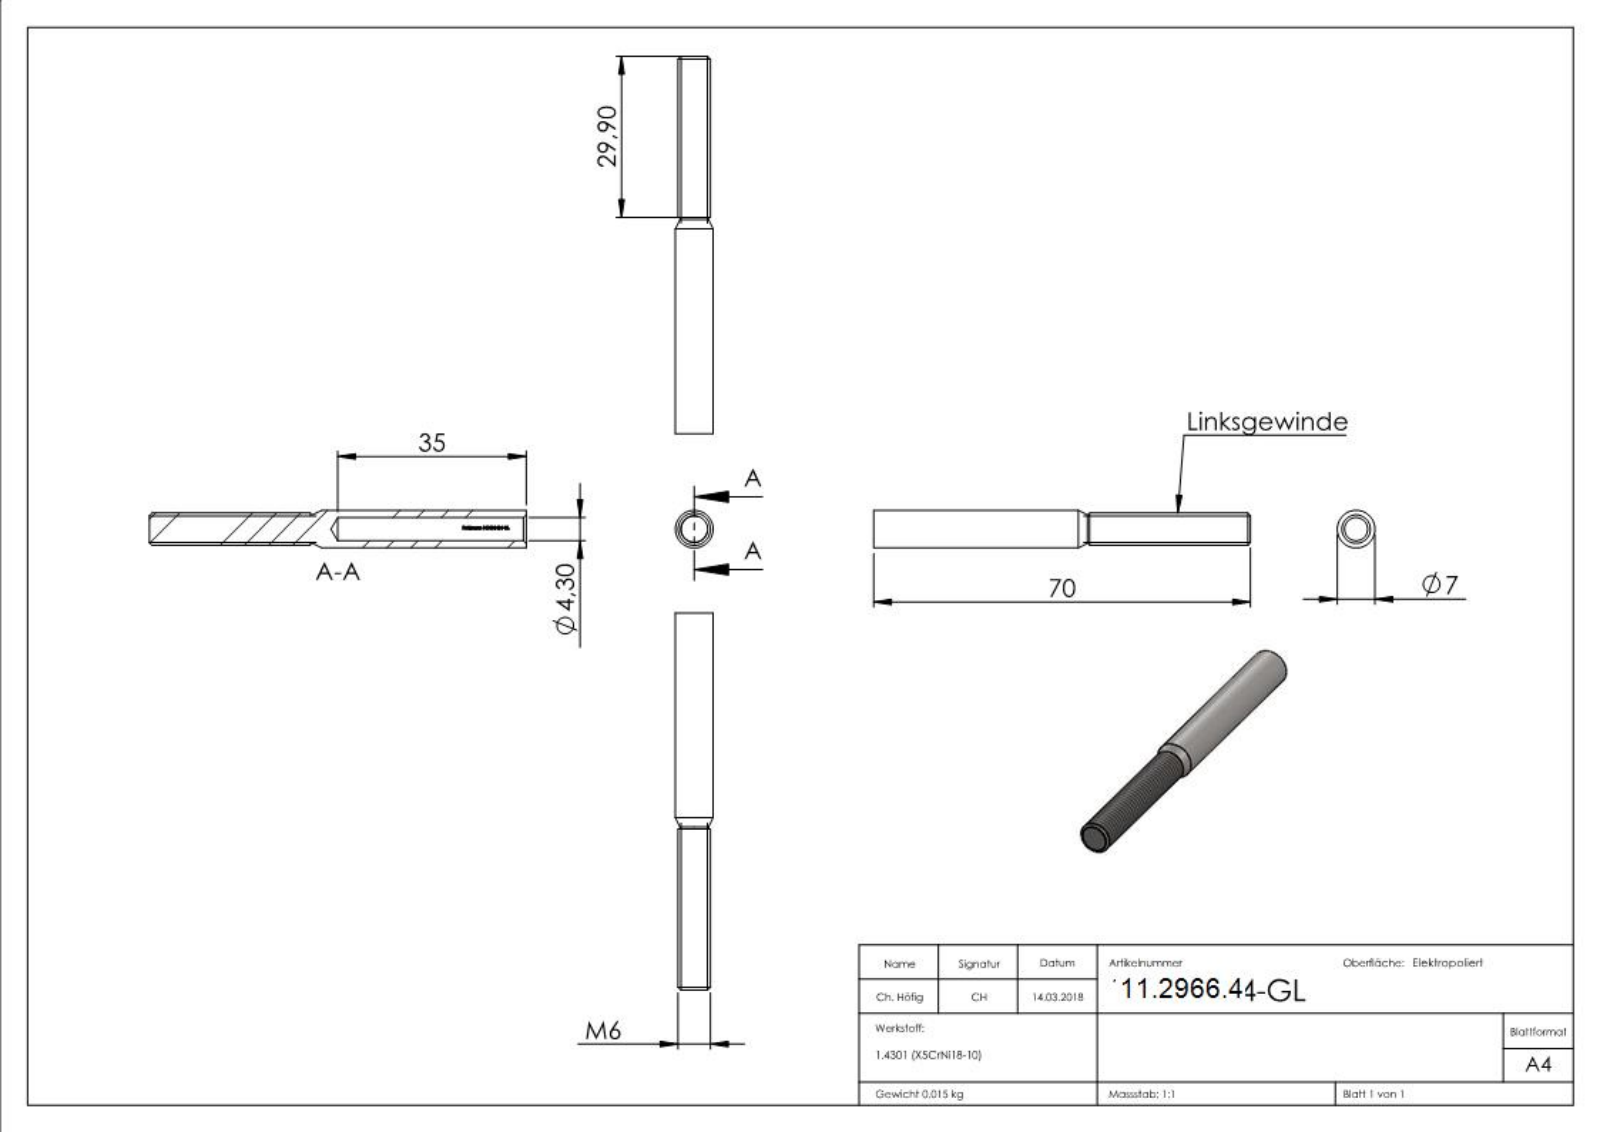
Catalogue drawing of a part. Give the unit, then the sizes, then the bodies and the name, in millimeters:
Units: millimetres
Overall size (bounding box): 70 × 7 × 7
Round holes (diameter × count): ⌀4.3 ×1
Round bosses / shafts (diameter × count): ⌀7 ×1, ⌀6 ×1, ⌀5.3 ×1
Partial cylindrical surfaces — rounded edges, fillets, slot ends (radius × count): R2.25 ×1
Main face-to-face distances: 70, 40.1, 29.9, 0.82, 7.5, 3.07, 3.89, 2.53, 4.48, 3.4
Volume: 1 849 mm³ · Surface area: 1 986 mm²
Bodies: 1 solid, 257 faces (109 planar, 38 cylindrical, 110 other)
Part name (STEP PRODUCT): 101000404-GL
STEP written by: SolidWorks 2015 (CONFIG_CONTROL_DESIGN)
